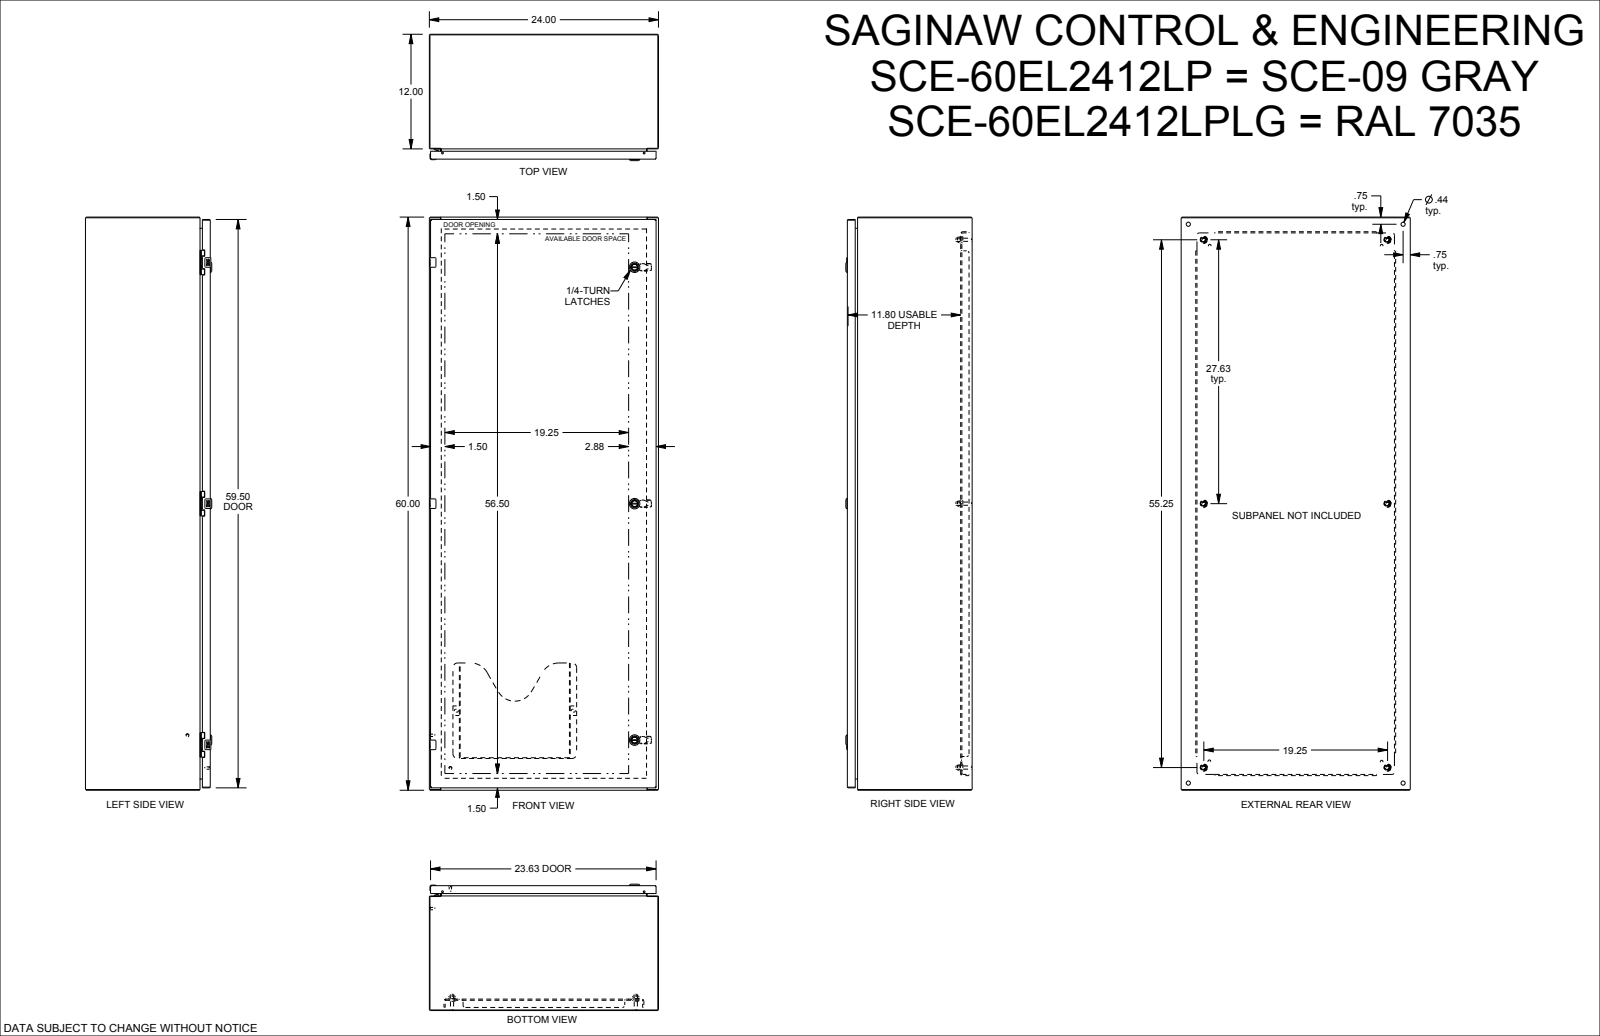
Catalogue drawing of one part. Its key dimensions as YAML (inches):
part_name: "SCE-60EL2412LP"
step_written_by: "SolidWorks 2021 (AUTOMOTIVE_DESIGN)"
units: inches
bodies: {solids: 31, faces: 1821, planar: 861, cylindrical: 671, other: 289}
overall_size: [60, 24, 13.225]
volume: 578.6
surface_area: 13890
round_holes:
  - {diameter: 0.205, count: 6}
  - {diameter: 0.5, count: 6}
  - {diameter: 0.375, count: 5}
  - {diameter: 0.281, count: 4}
  - {diameter: 0.437, count: 4}
  - {diameter: 0.04, count: 3}
  - {diameter: 0.197, count: 3}
  - {diameter: 0.218, count: 3}
  - {diameter: 0.394, count: 3}
  - {diameter: 0.634, count: 3}
  - {diameter: 0.188, count: 2}
  - {diameter: 0.204, count: 1}
round_bosses_or_shafts:
  - {diameter: 0.375, count: 6}
  - {diameter: 0.33, count: 6}
  - {diameter: 0.24, count: 6}
  - {diameter: 1.102, count: 3}
  - {diameter: 0.78, count: 3}
  - {diameter: 0.63, count: 3}
  - {diameter: 0.504, count: 3}
  - {diameter: 0.39, count: 3}
partial_cylinders:
  - {radius: 0.015, count: 28}
  - {radius: 0.04, count: 17}
  - {radius: 0.22, count: 16}
  - {radius: 0.031, count: 14}
  - {radius: 0.043, count: 12}
  - {radius: 0.062, count: 12}
  - {radius: 0.1, count: 12}
  - {radius: 0.118, count: 12}
face_to_face_distances: [0.075, 0.06, 12.993, 23.925, 13.068, 13.008, 12.933, 1.125, 1.2, 11.868]
hole_center_spacings: [25.25, 0.494, 2.299, 20.938, 24.758, 25.742, 27.625, 29.296]
